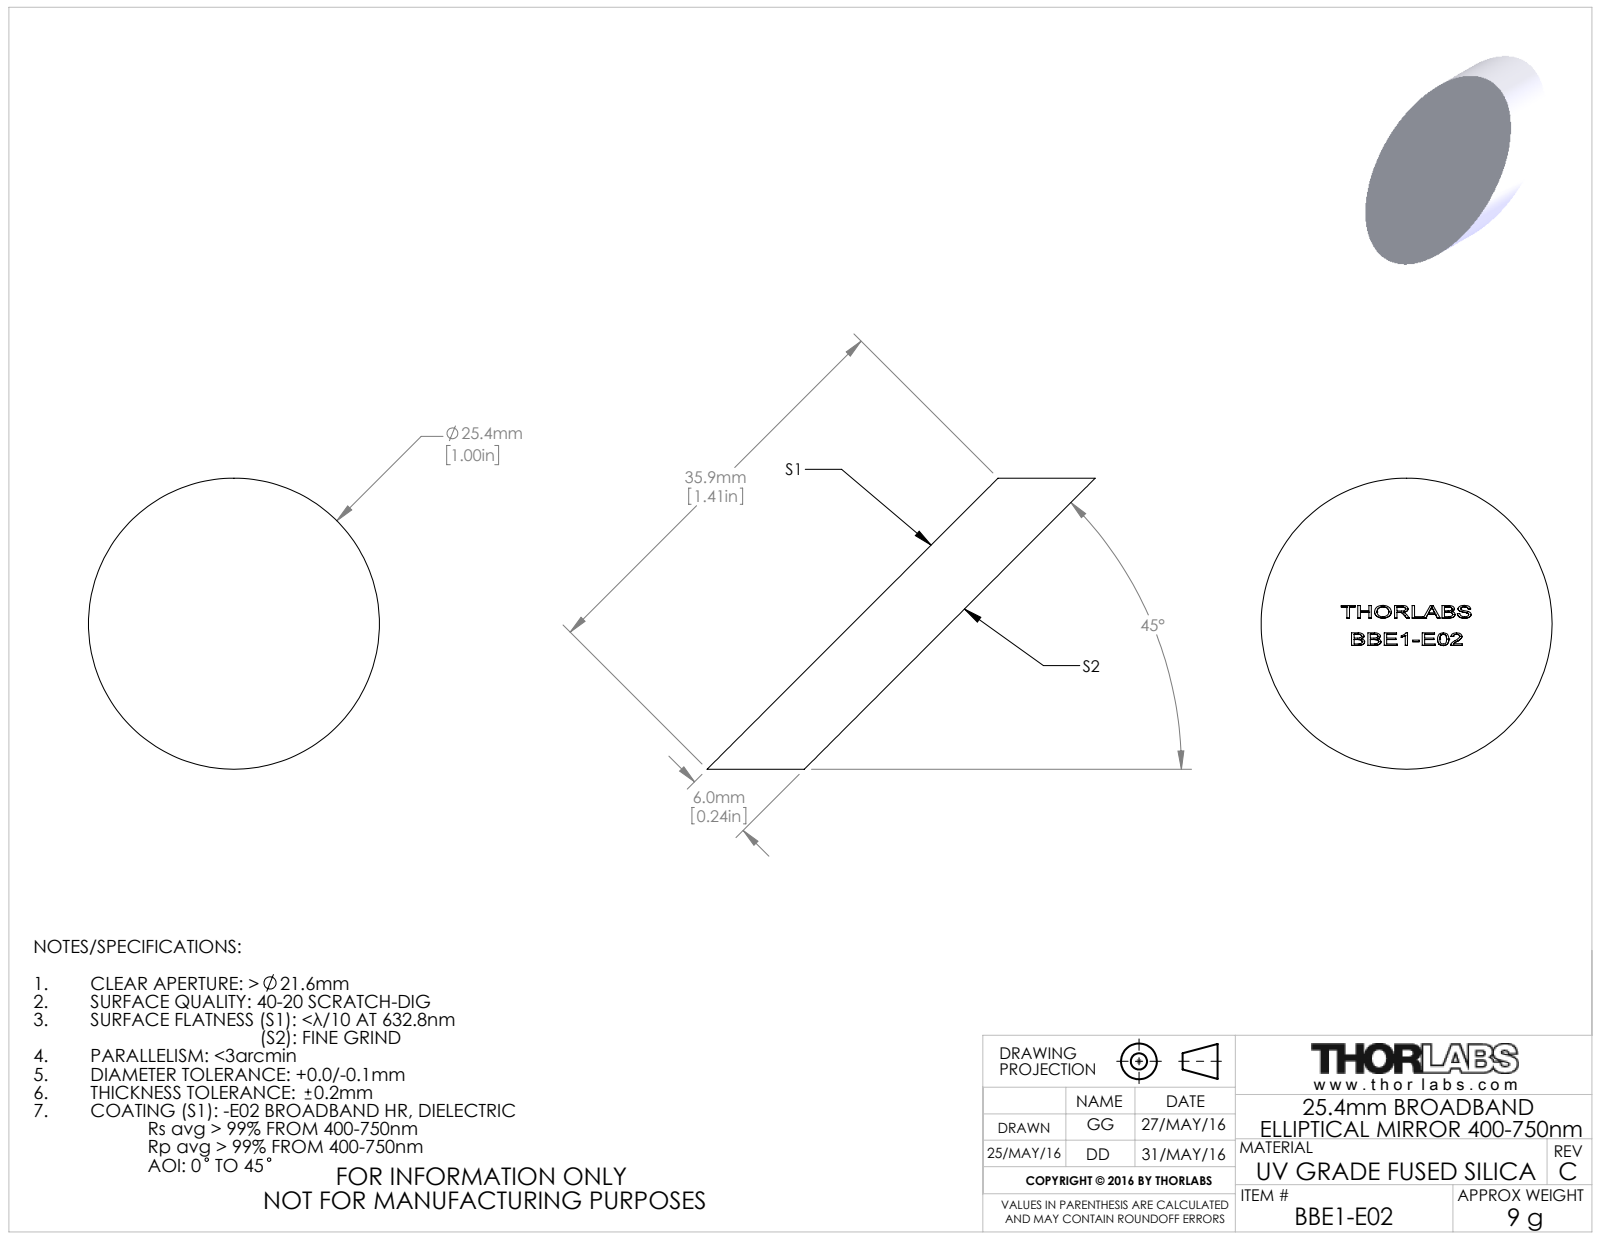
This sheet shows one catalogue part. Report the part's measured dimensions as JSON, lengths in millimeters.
{"part_name": "21546-E0W", "step_written_by": "SolidWorks 2009 (AUTOMOTIVE_DESIGN)", "units": "millimeters", "bodies": {"solids": 1, "faces": 227, "planar": 142, "cylindrical": 2, "other": 83}, "overall_size": [33.88, 25.4, 25.4], "volume_mm3": 4299, "surface_area_mm2": 2110, "round_bosses_or_shafts": [[25.4, 1]], "face_to_face_distances": [6, 3.37, 1.54, 1.36, 0.71, 0.65, 1.83, 2.66, 3.55, 4.15]}
